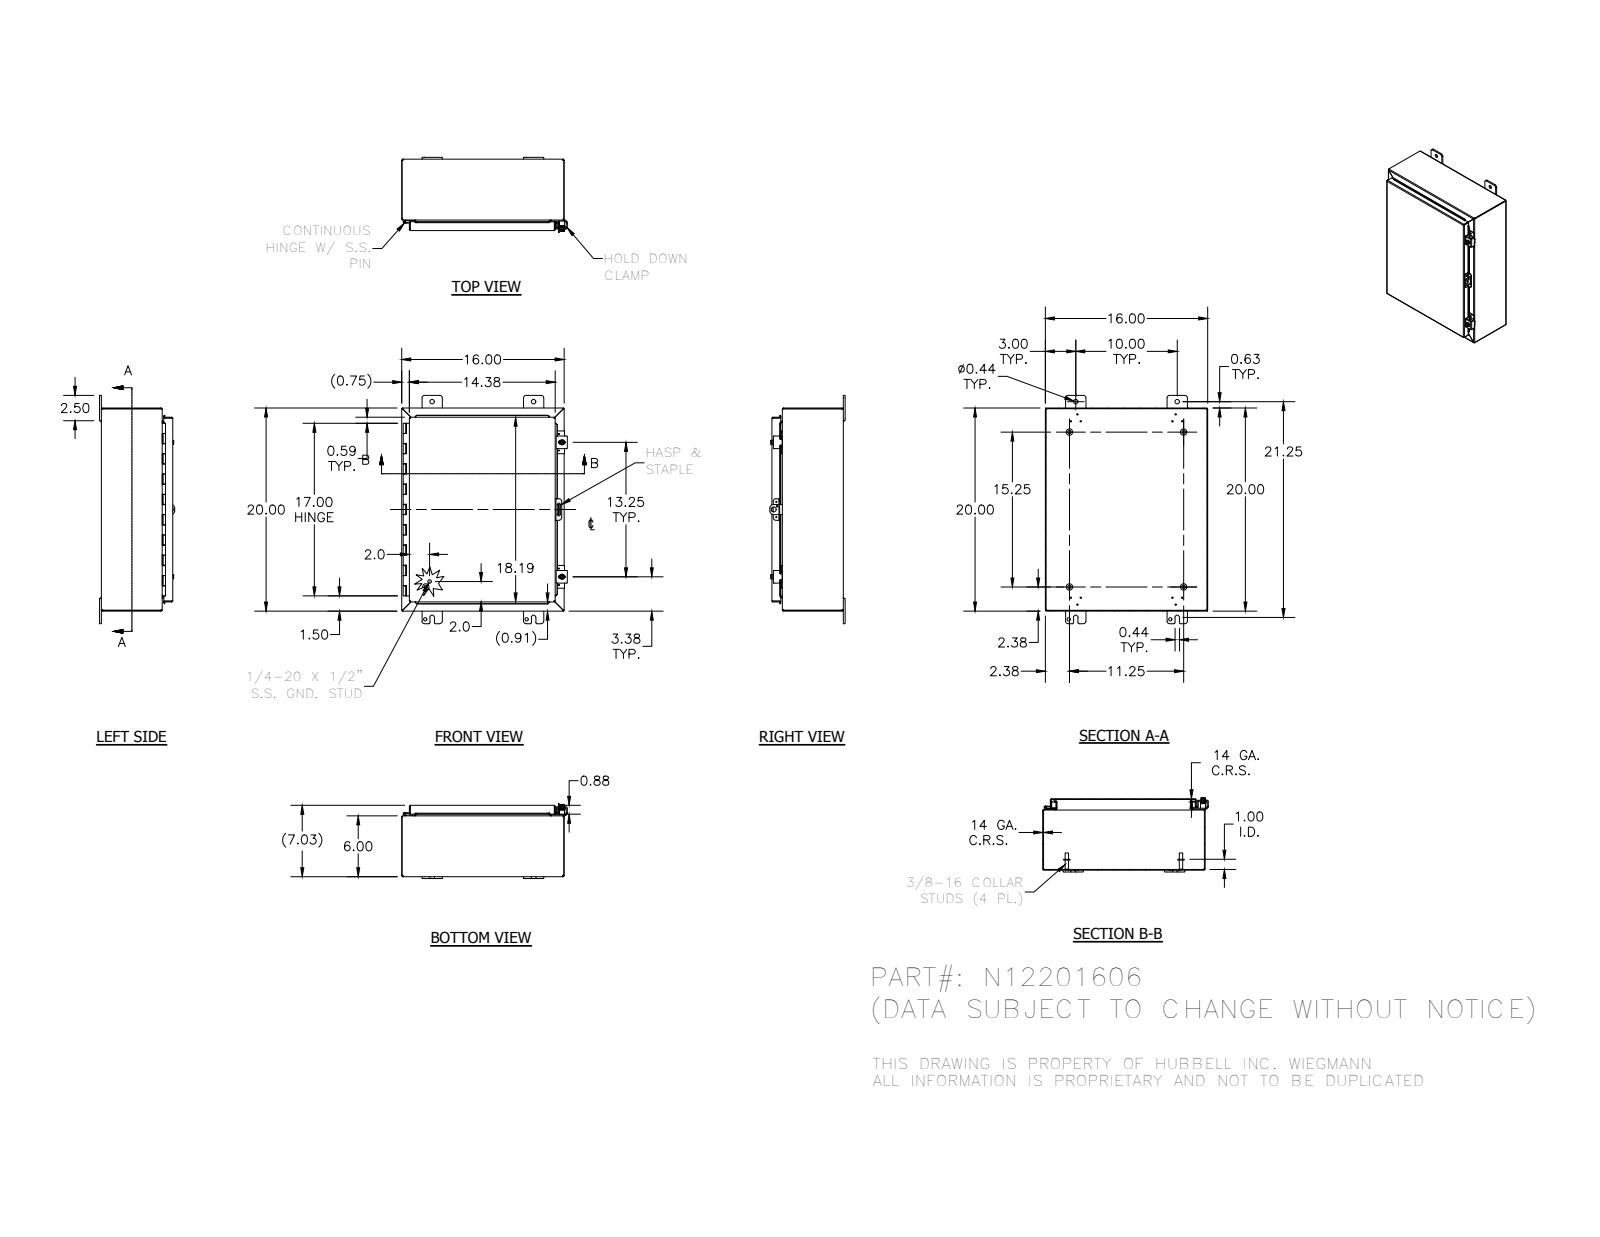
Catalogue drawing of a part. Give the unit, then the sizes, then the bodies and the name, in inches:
Units: inches
Overall size (bounding box): 22.5 × 16.311 × 7.41
Round holes (diameter × count): ⌀0.12 ×12, ⌀0.11 ×7, ⌀0.313 ×4, ⌀0.438 ×4, ⌀0.211 ×2, ⌀0.281 ×2, ⌀0.3 ×2, ⌀0.125 ×1, ⌀0.156 ×1, ⌀0.5 ×1
Round bosses / shafts (diameter × count): ⌀0.625 ×4, ⌀0.33 ×4, ⌀0.25 ×4, ⌀0.52 ×2, ⌀0.5 ×2, ⌀0.35 ×2, ⌀0.115 ×2, ⌀0.337 ×1
Partial cylindrical surfaces — rounded edges, fillets, slot ends (radius × count): R0.03 ×27, R0.063 ×25, R0.125 ×25, R0.25 ×25, R0.031 ×23, R0.105 ×23, R0.07 ×8, R0.1 ×4
Main face-to-face distances: 0.074, 6.959, 6.885, 7.033, 15.926, 19.926, 5.926, 1.033, 15.852, 16
Hole centre spacings: 10, 0.759, 0.839, 0.94, 0.969, 1.593, 1.995, 9.382
Volume: 103.7 in³ · Surface area: 2 679 in²
Bodies: 27 solids, 948 faces (511 planar, 320 cylindrical, 117 other)
Part name (STEP PRODUCT): N12201606; 34840; 38420; N12201606BKP (+8 more)
STEP written by: Autodesk Inventor 2012 (AUTOMOTIVE_DESIGN)
